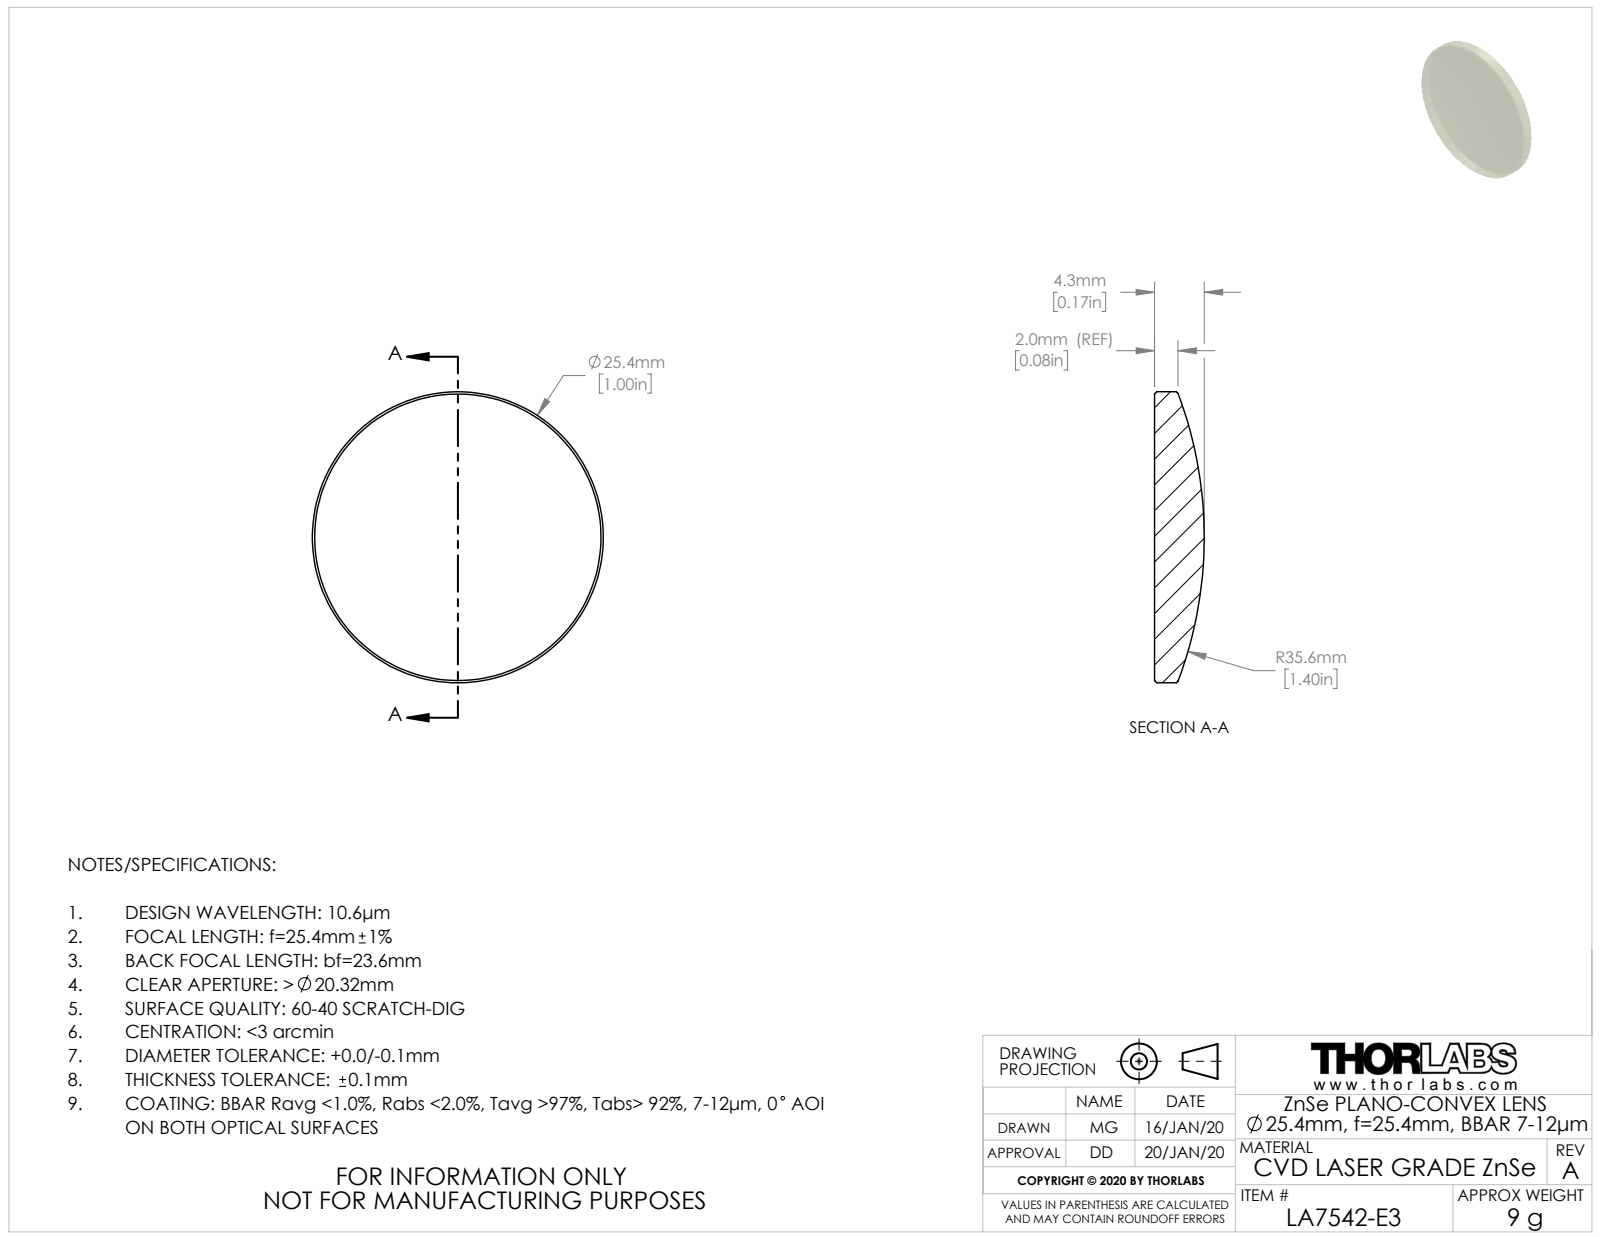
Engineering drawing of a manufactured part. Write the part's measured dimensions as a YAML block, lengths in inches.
part_name: "TTN206023-E0W"
step_written_by: "SolidWorks 2018 (CONFIG_CONTROL_DESIGN)"
units: inches
bodies: {solids: 1, faces: 9, planar: 1, cylindrical: 2, other: 6}
overall_size: [1, 1, 0.171]
volume: 0.098
surface_area: 1.826
round_bosses_or_shafts:
  - {diameter: 1, count: 1}
